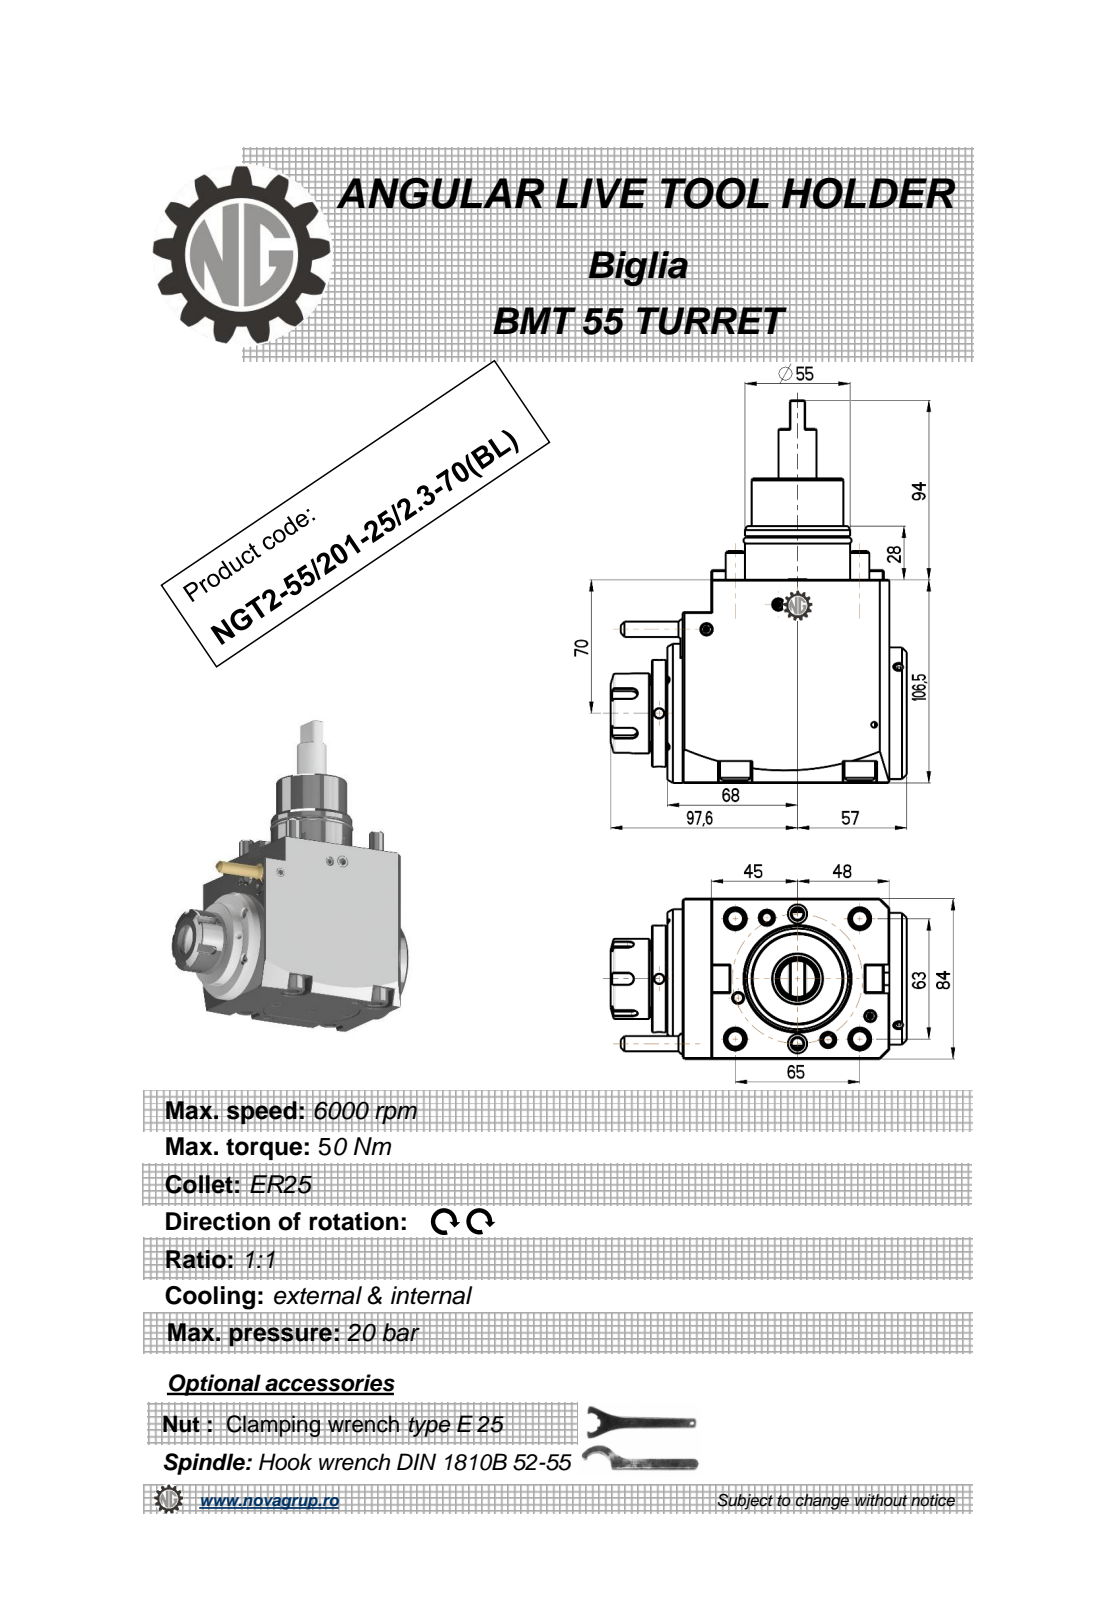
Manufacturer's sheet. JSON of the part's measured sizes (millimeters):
{"part_name": "NGT2_55_201_25_1_3_70_BL", "step_written_by": "PRO/ENGINEER BY PARAMETRIC TECHNOLOGY CORPORATION, 2010280 (CONFIG_CONTROL_DESIGN)", "units": "millimeters", "bodies": {"solids": 2, "faces": 454, "planar": 204, "cylindrical": 112, "other": 138}, "overall_size": [200.5, 155.6, 84], "volume_mm3": 1179000, "surface_area_mm2": 89978, "round_holes": [[5, 3], [6, 2], [3, 1]], "round_bosses_or_shafts": [[16, 4], [10, 4], [73, 1], [69, 1], [56, 1], [55, 1], [50, 1], [48, 1]], "partial_cylinders_radius": [[0.32, 20], [0.22, 6], [3, 5], [8.5, 4], [0.8, 2], [480, 2], [3.4, 1], [4, 1]], "face_to_face_distances": [84, 106.5, 8, 9, 118, 16, 109, 117, 126, 53], "hole_center_spacings": [80.76, 68]}
